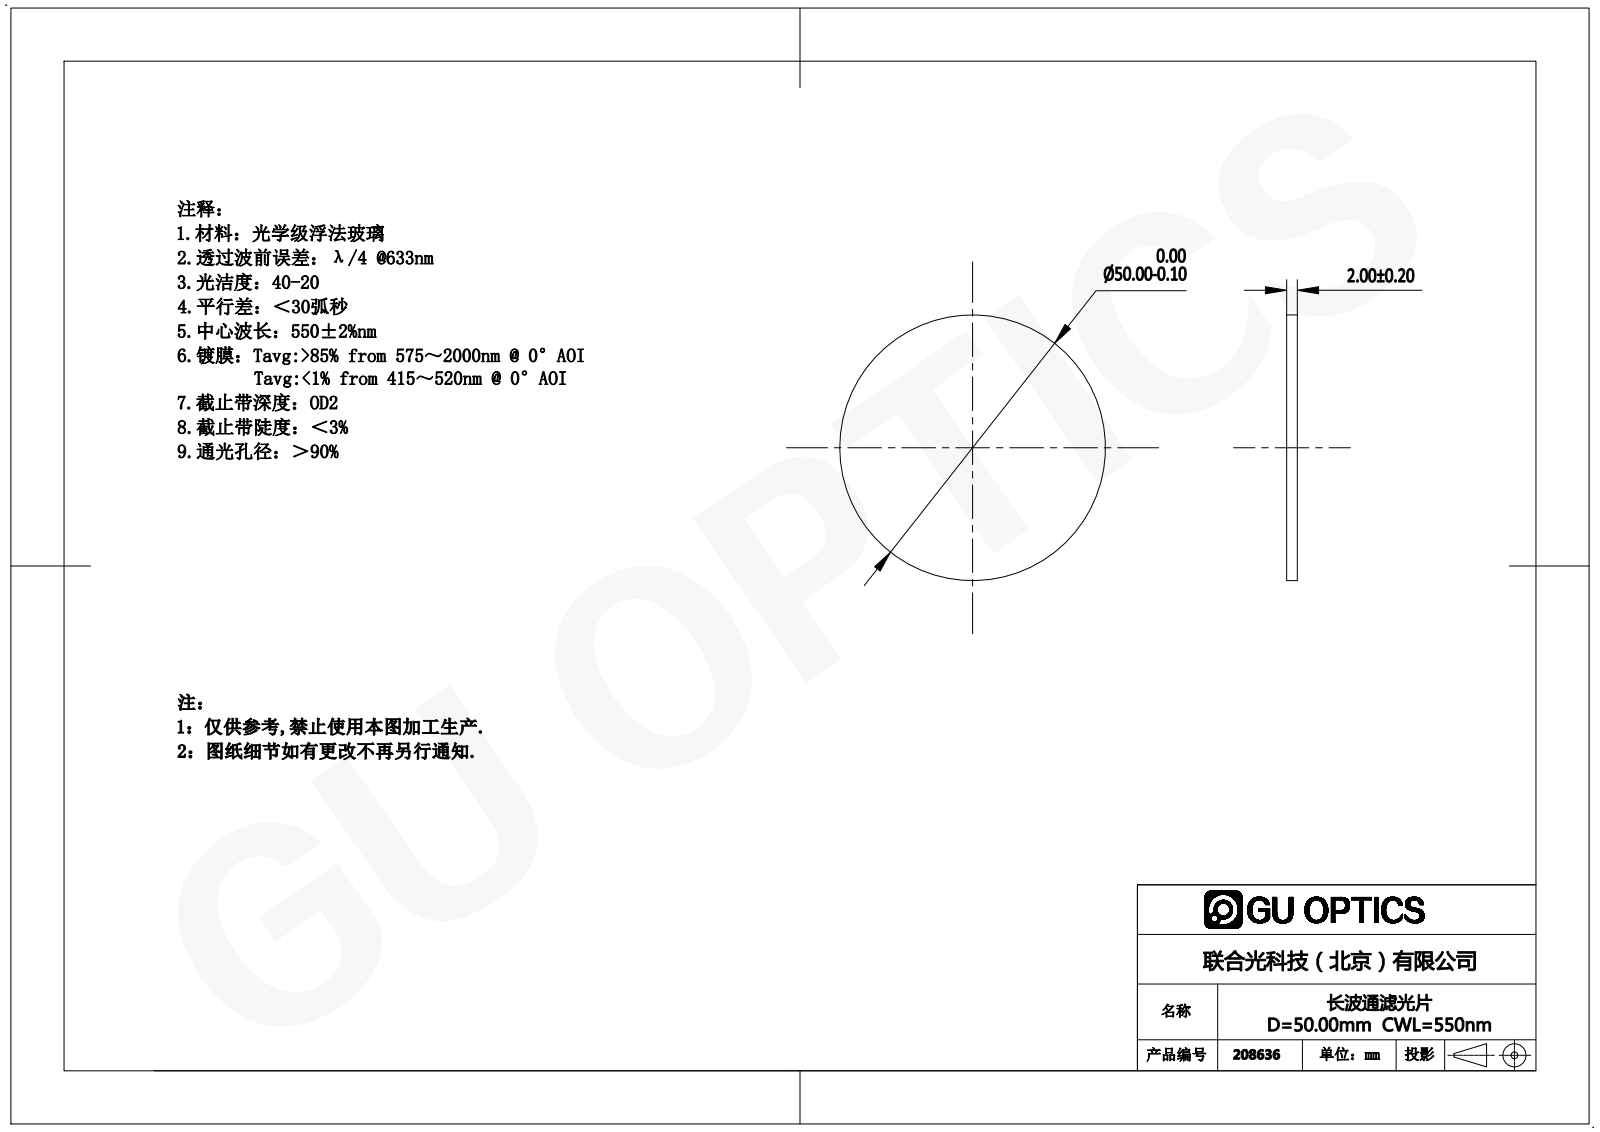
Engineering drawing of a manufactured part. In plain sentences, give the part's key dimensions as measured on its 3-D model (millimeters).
The part is named "208633". Its 3-D file was written by "SolidWorks 2016 (AUTOMOTIVE_DESIGN)". It is 1 solid with 4 faces: 2 planar, 2 cylindrical and 0 other. Overall it measures 50 by 50 by 2 millimeters. Its volume is 3 927 cubic millimeters and its surface area 4 241 square millimeters. Round bosses or shafts: 1 of diameter 50. The main face-to-face distances are 2.
